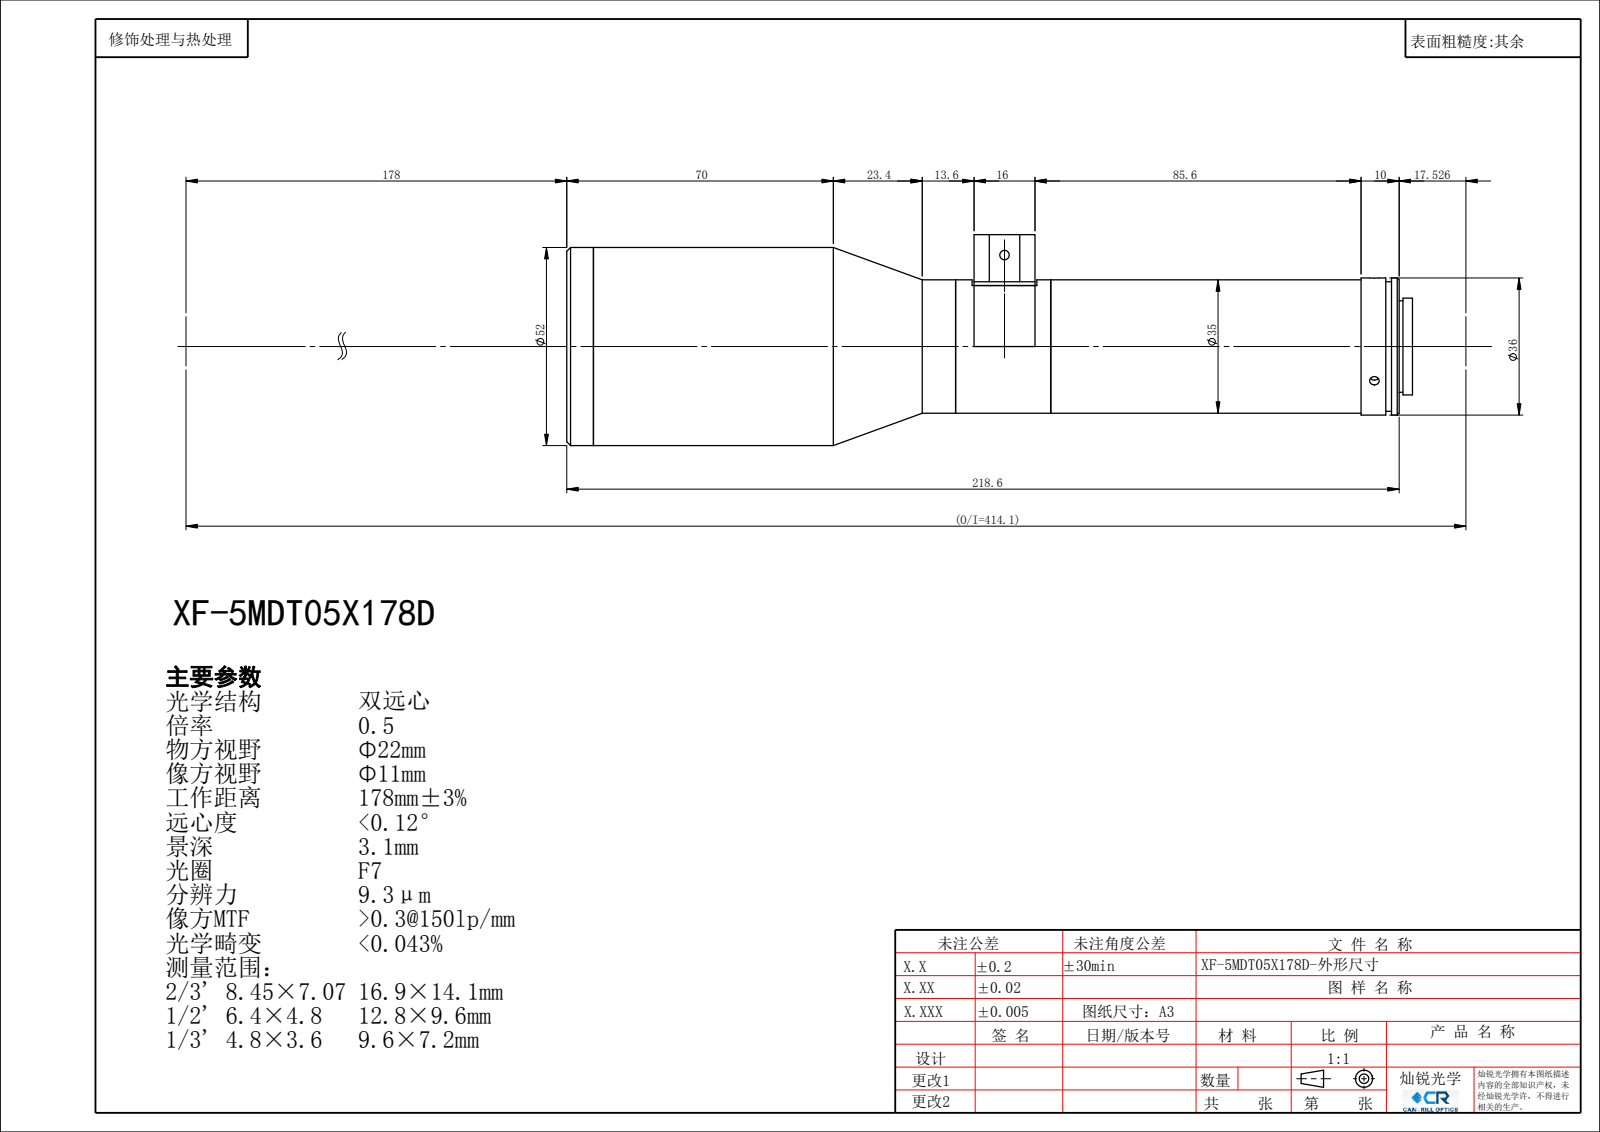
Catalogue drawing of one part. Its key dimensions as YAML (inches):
part_name: "XF-5MDT05X178D"
step_written_by: "SolidWorks 2014 (CONFIG_CONTROL_DESIGN)"
units: inches
bodies: {solids: 0, faces: 116, planar: 39, cylindrical: 67, other: 10}
overall_size: [8.743, 2.179, 2.047]
round_holes:
  - {diameter: 0.063, count: 4}
  - {diameter: 0.087, count: 4}
  - {diameter: 0.098, count: 4}
  - {diameter: 0.551, count: 1}
  - {diameter: 0.843, count: 1}
  - {diameter: 1.024, count: 1}
  - {diameter: 1.575, count: 1}
  - {diameter: 1.748, count: 1}
  - {diameter: 1.89, count: 1}
round_bosses_or_shafts:
  - {diameter: 2.047, count: 1}
  - {diameter: 1.417, count: 1}
  - {diameter: 1.378, count: 1}
  - {diameter: 1.339, count: 1}
  - {diameter: 1.102, count: 1}
  - {diameter: 1, count: 1}
  - {diameter: 0.945, count: 1}
partial_cylinders:
  - {radius: 0.157, count: 4}
face_to_face_distances: [0.276, 3.744, 4.728, 0.984, 8.33, 4.586, 3.602, 4.02, 5.004, 8.606]
hole_center_spacings: [0.629, 0.433, 1.181, 1.258, 3.656, 4.083, 3.824]
